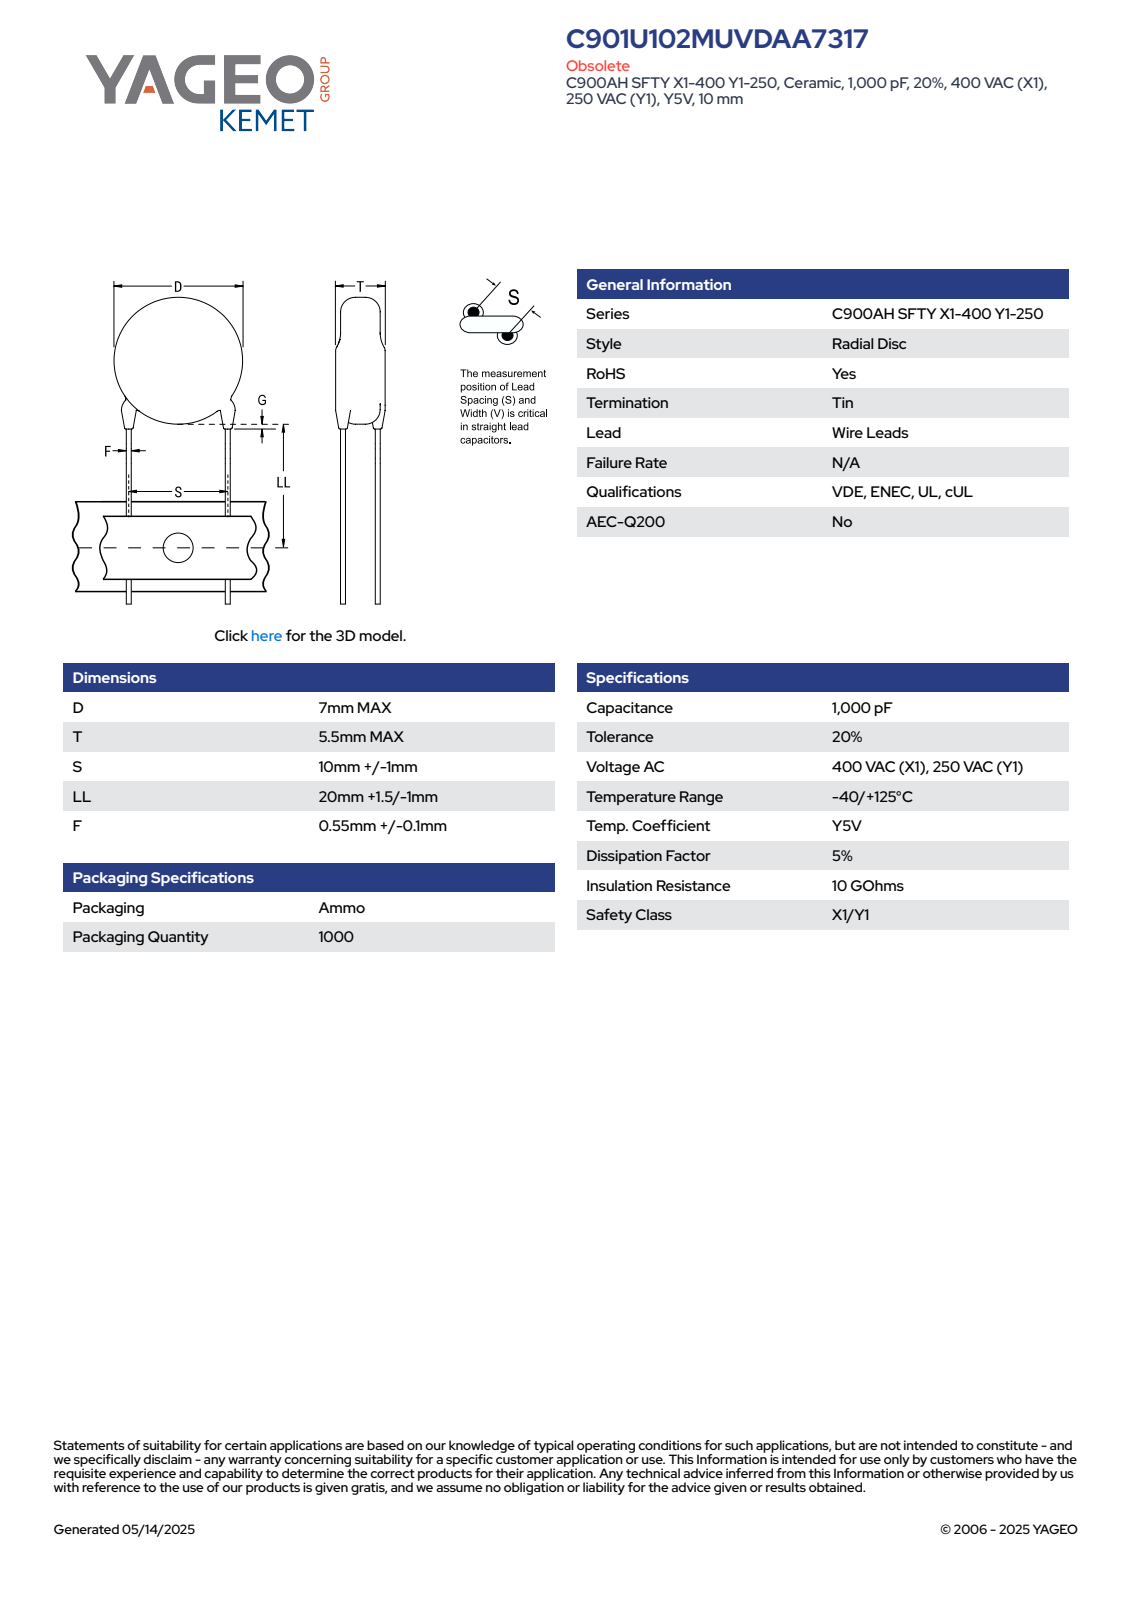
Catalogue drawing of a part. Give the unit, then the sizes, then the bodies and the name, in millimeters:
Units: millimetres
Overall size (bounding box): 28.5 × 8.77 × 6.92
Round bosses / shafts (diameter × count): ⌀0.65 ×2, ⌀7 ×1
Main face-to-face distances: 5.5, 0.81, 25.4, 24.59, 3.3, 1.67, 3.52, 2.4, 2.49, 1.32
Volume: 222 mm³ · Surface area: 284 mm²
Bodies: 4 solids, 83 faces (61 planar, 6 cylindrical, 16 other)
Part name (STEP PRODUCT): CCD_STC900_D7T5.5S10LL21.5F0.65G3
STEP written by: SolidWorks 2014 (AUTOMOTIVE_DESIGN)
